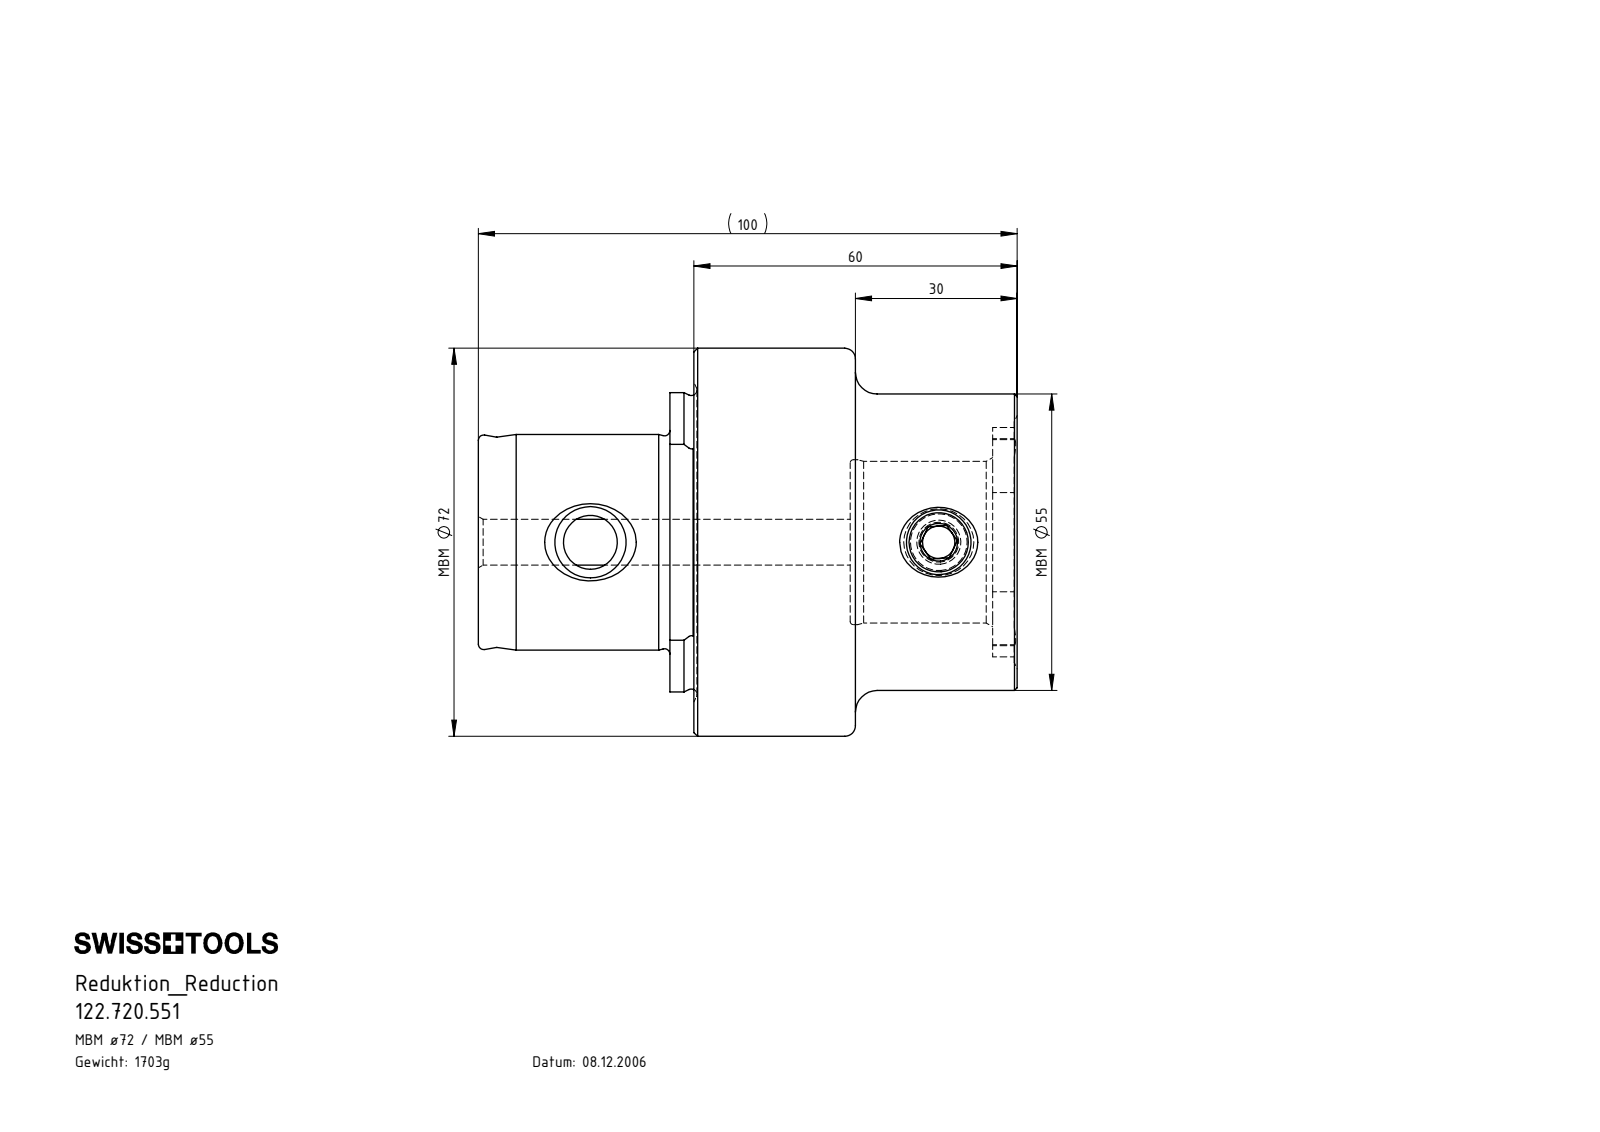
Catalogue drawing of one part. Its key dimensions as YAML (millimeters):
part_name: "MB7-MB5.K01.060_C; 122.720.551; MB5-ER1.001.017_A"
step_written_by: "SolidWorks 2017 (CONFIG_CONTROL_DESIGN)"
units: millimeters
bodies: {solids: 2, faces: 137, planar: 35, cylindrical: 35, other: 67}
overall_size: [100, 72, 72]
volume: 216912
surface_area: 30908
round_holes:
  - {diameter: 6, count: 1}
  - {diameter: 8.5, count: 1}
  - {diameter: 10, count: 1}
  - {diameter: 11, count: 1}
  - {diameter: 30, count: 1}
  - {diameter: 30.6, count: 1}
round_bosses_or_shafts:
  - {diameter: 72, count: 1}
  - {diameter: 55, count: 1}
  - {diameter: 40, count: 1}
  - {diameter: 12, count: 1}
partial_cylinders:
  - {radius: 5.2, count: 4}
  - {radius: 18.5, count: 1}
  - {radius: 21.27, count: 1}
  - {radius: 27.77, count: 1}
face_to_face_distances: [40, 30, 4.45, 35.55, 69, 33.45, 29, 100, 64.45, 60]
hole_center_spacings: [64.65]
